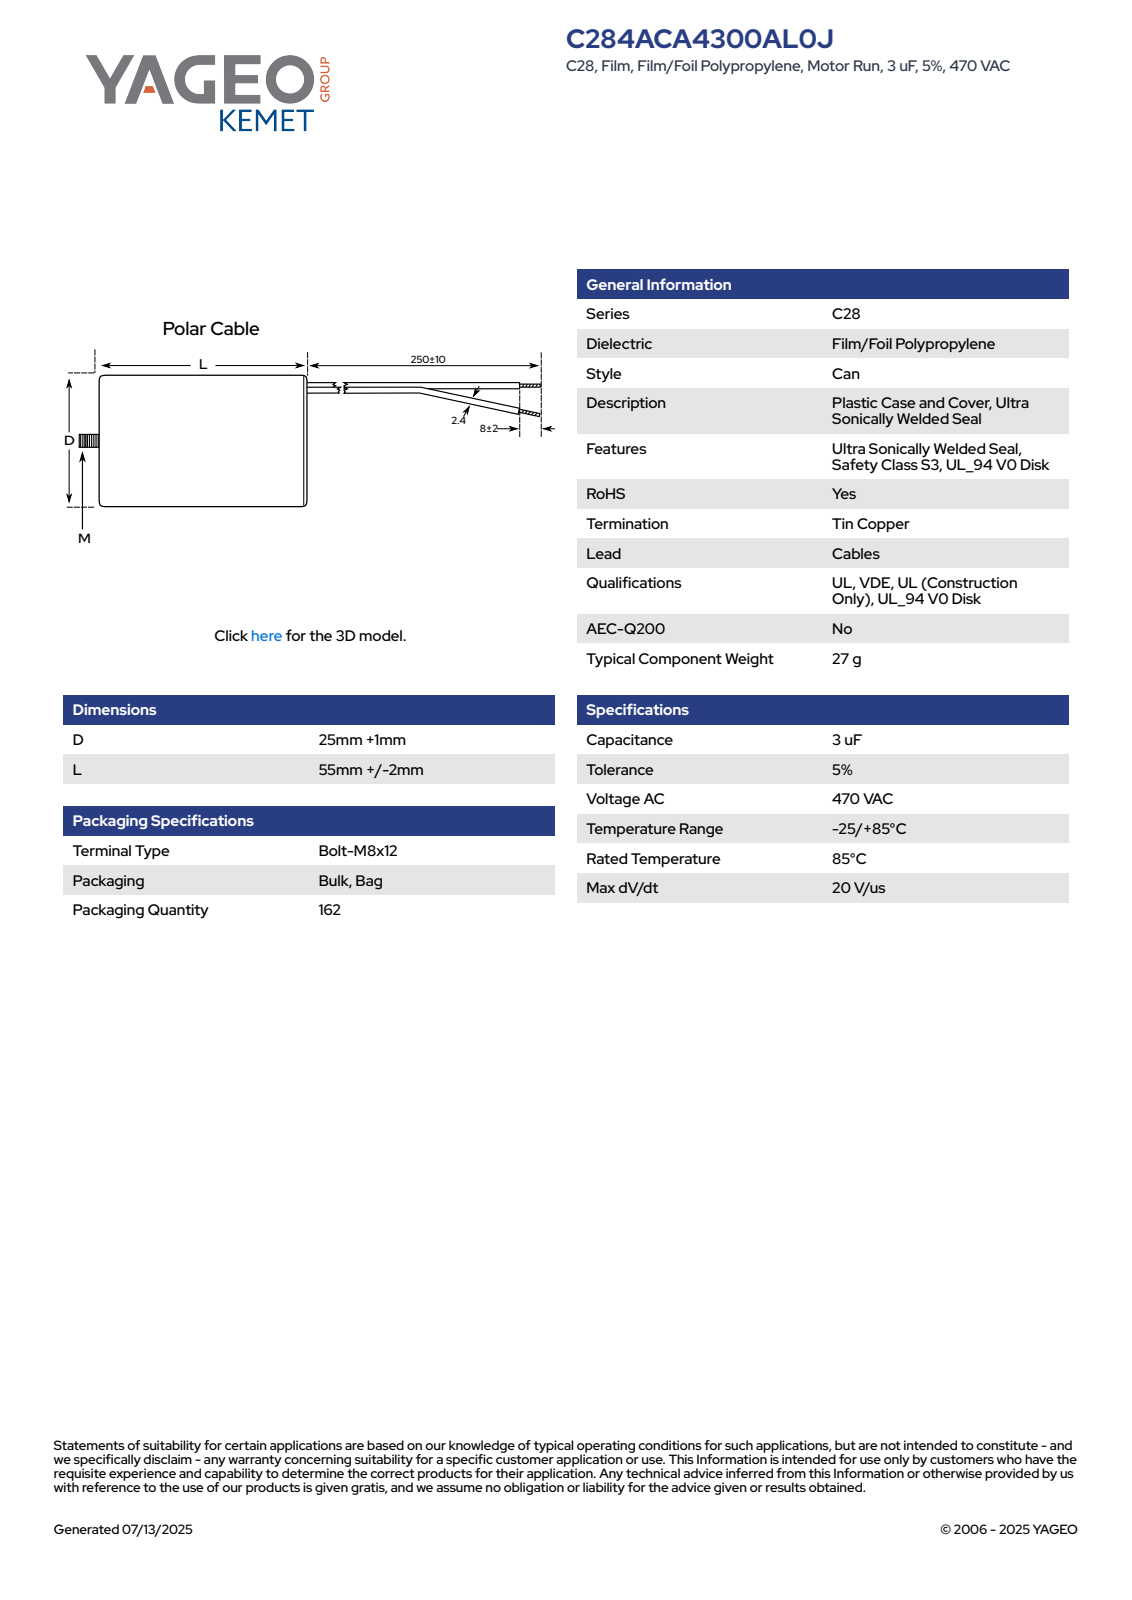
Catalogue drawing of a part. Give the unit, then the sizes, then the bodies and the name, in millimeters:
Units: millimetres
Overall size (bounding box): 67 × 26.01 × 26
Round holes (diameter × count): ⌀22 ×1
Round bosses / shafts (diameter × count): ⌀26 ×1, ⌀8 ×1
Partial cylindrical surfaces — rounded edges, fillets, slot ends (radius × count): R13.01 ×1
Main face-to-face distances: 55, 57, 2, 10, 65, 67
Volume: 29 972 mm³ · Surface area: 6 038 mm²
Bodies: 1 solid, 76 faces (26 planar, 15 cylindrical, 35 other)
Part name (STEP PRODUCT): CFM_C28P_25X55_D26L57
STEP written by: SolidWorks 2021 (AUTOMOTIVE_DESIGN)
